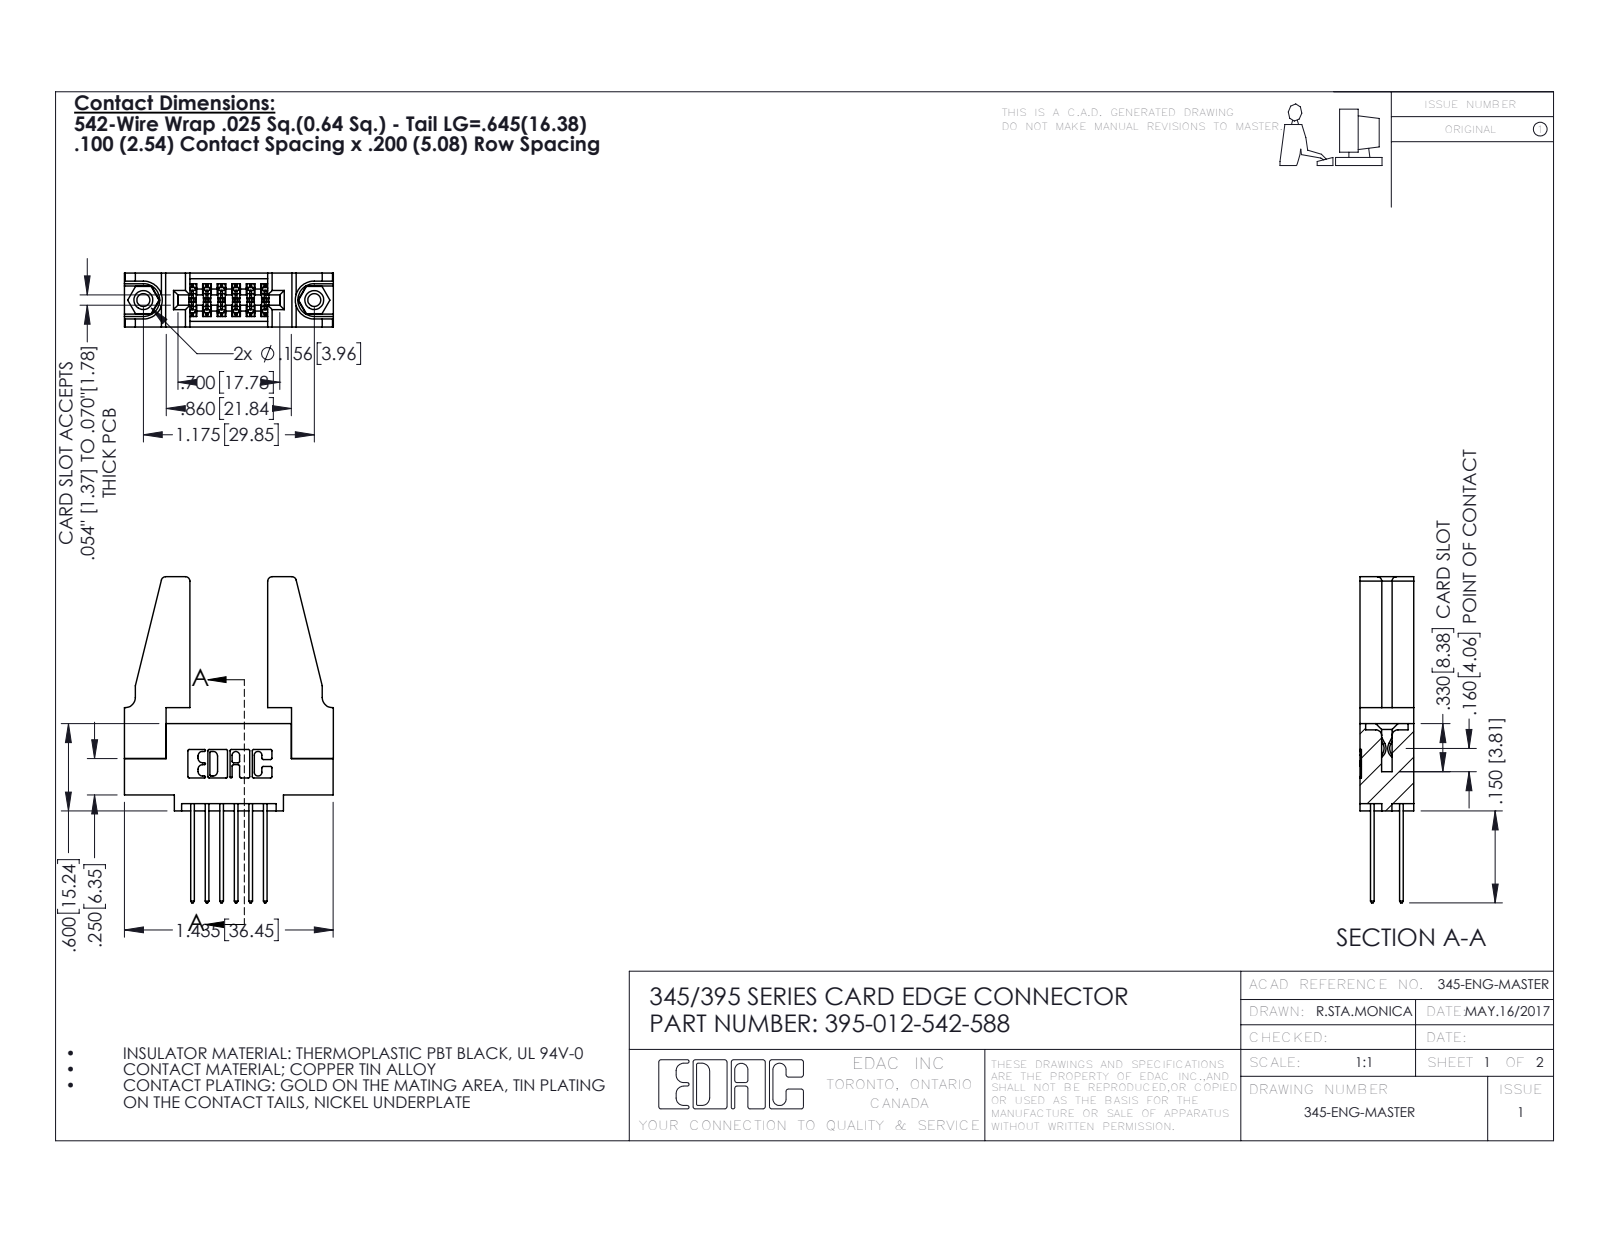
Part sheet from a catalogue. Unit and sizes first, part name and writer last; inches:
Units: inches
Overall size (bounding box): 2.242 × 1.436 × 0.37
Round holes (diameter × count): ⌀0.089 ×2, ⌀0.125 ×2, ⌀0.156 ×2, ⌀0.064 ×1
Round bosses / shafts (diameter × count): ⌀0.155 ×2
Partial cylindrical surfaces — rounded edges, fillets, slot ends (radius × count): R0.01 ×22, R0.006 ×18, R0.01 ×12, R0.03 ×8, R0.007 ×6, R0.031 ×6, R0.026 ×3, R0.014 ×2
Main face-to-face distances: 0.37, 0.072, 0.298, 0.2, 0.098, 0.272, 0.025, 0.225, 0.15, 0.148
Hole centre spacings: 0.27, 0.946, 1.175
Volume: 0.393 in³ · Surface area: 11.62 in²
Bodies: 17 solids, 854 faces (552 planar, 286 cylindrical, 16 other)
Part name (STEP PRODUCT): 345 Part_0.110 Offset - 0.156 Dia-TH; 345-220-078_345-220-088; 345-250-001_345-250-001-102; 345-292-001_345-293-142 (+1 more)
STEP written by: SolidWorks 2016 (CONFIG_CONTROL_DESIGN)
